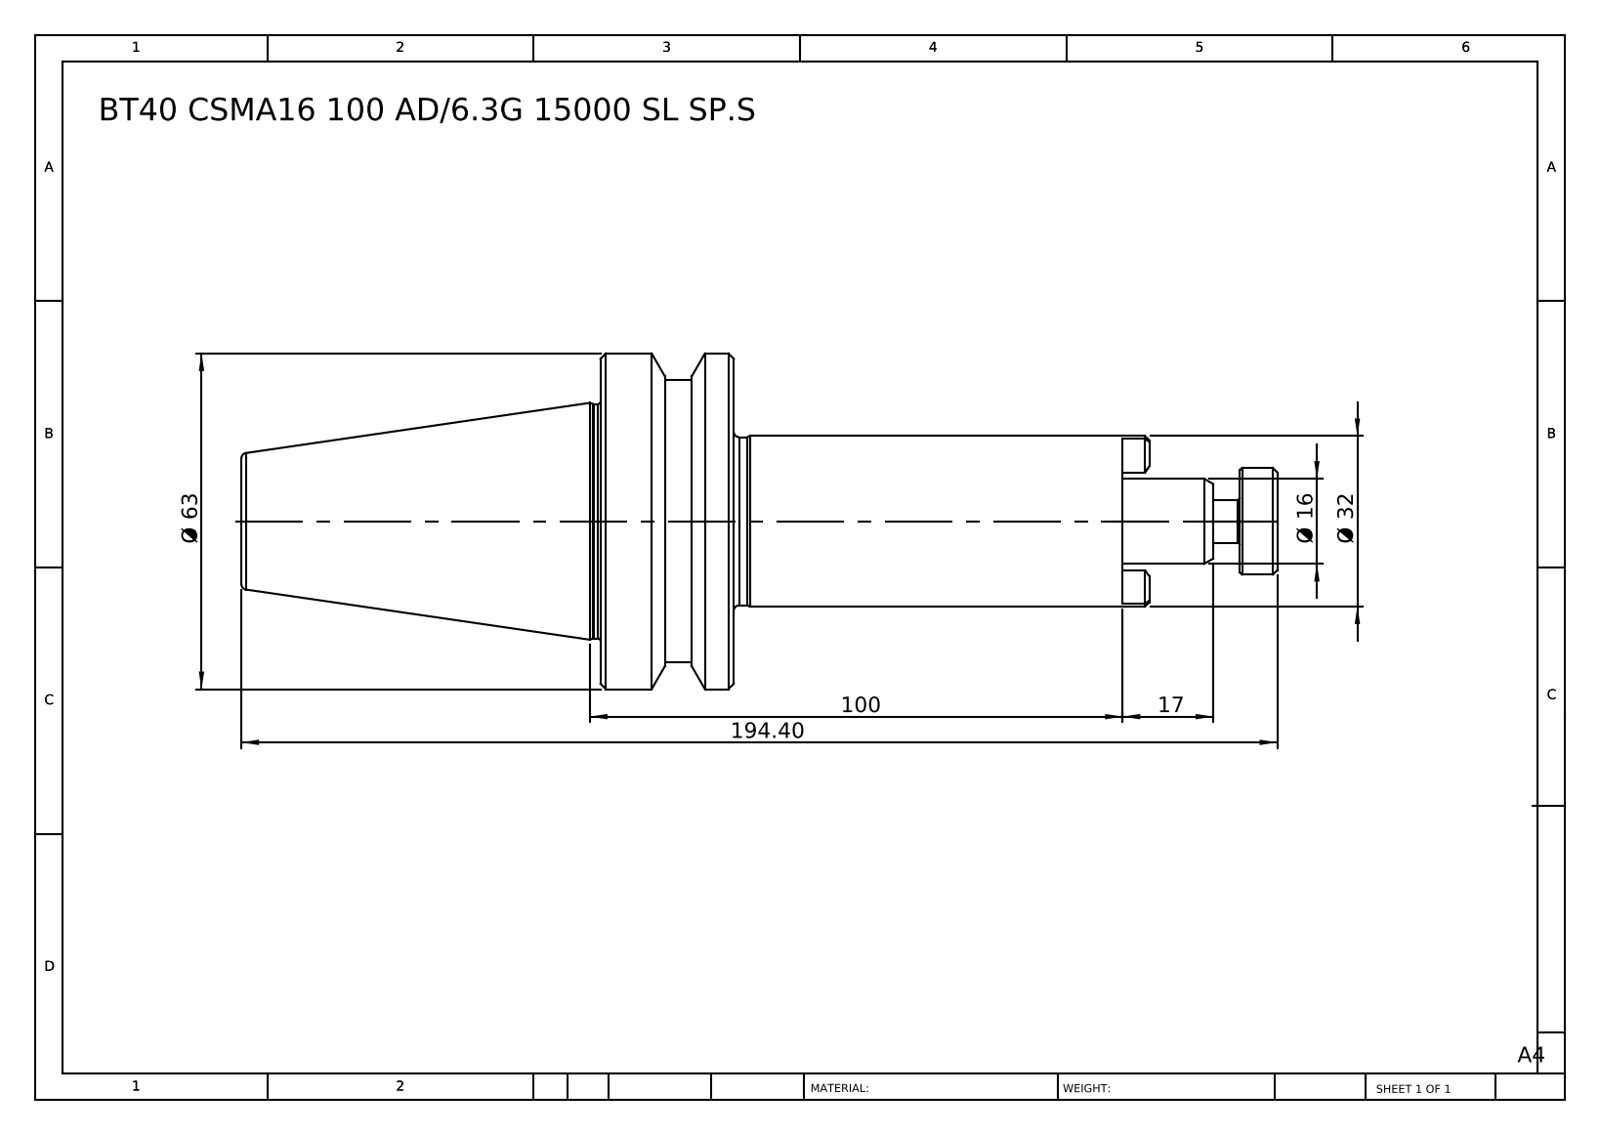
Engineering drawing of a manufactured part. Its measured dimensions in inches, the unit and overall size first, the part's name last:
Units: inches
Overall size (bounding box): 7.654 × 2.48 × 2.48
Round holes (diameter × count): ⌀0.787 ×1
Round bosses / shafts (diameter × count): ⌀2.48 ×1, ⌀2.087 ×1, ⌀1.732 ×1, ⌀1.26 ×1, ⌀1.244 ×1, ⌀0.63 ×1, ⌀0.315 ×1
Main face-to-face distances: 0.984, 2.874, 3.858, 6.512, 3.638, 2.654, 0.197, 1.142, 4.016, 5
Volume: 12.41 in³ · Surface area: 43.04 in²
Bodies: 1 solid, 74 faces (19 planar, 21 cylindrical, 34 other)
Part name (STEP PRODUCT): BT40 CSMA16 100 AD-6.3G 15000 SL SP.S
STEP written by: SolidWorks 2014 (CONFIG_CONTROL_DESIGN)
